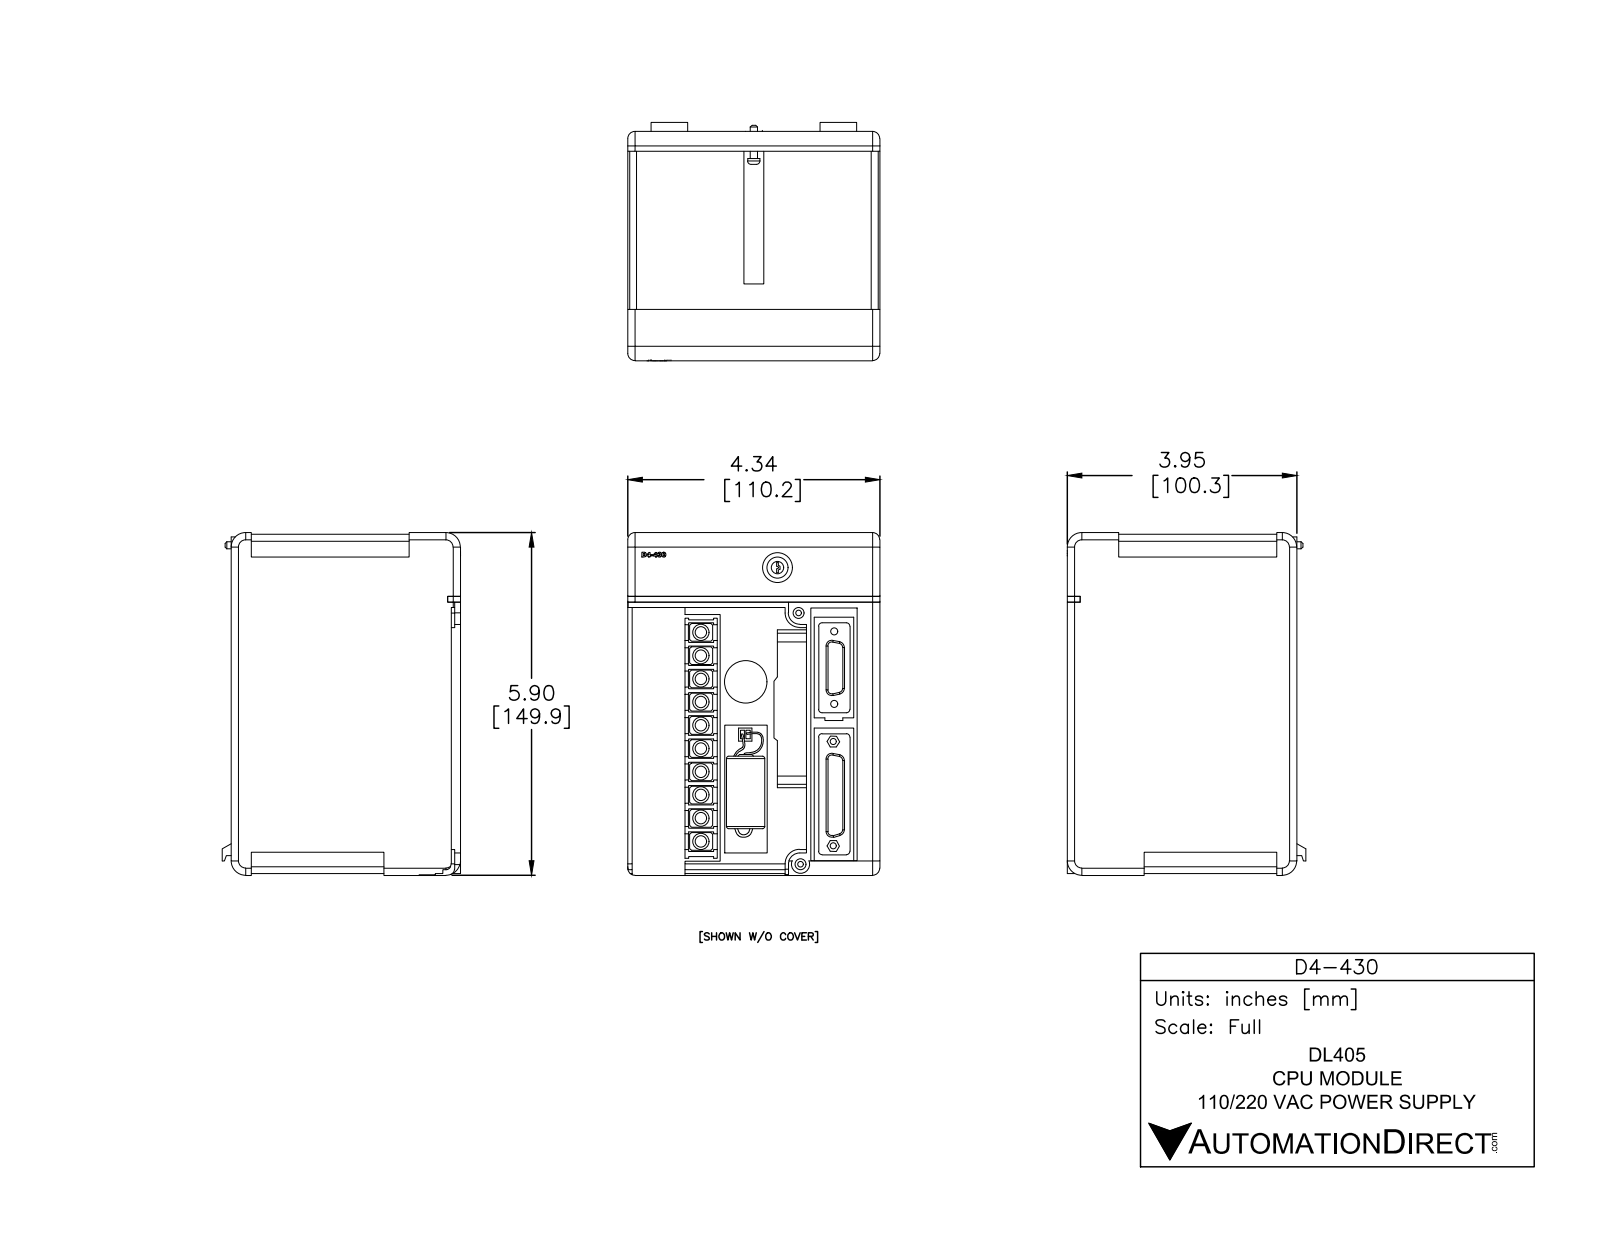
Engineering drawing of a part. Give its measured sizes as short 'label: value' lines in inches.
name: D4-430
written by: SolidWorks 2014 (AUTOMOTIVE_DESIGN)
unit: in
bodies: 2 solids, 755 faces (563 planar, 116 cylindrical, 76 other)
size: 5.905 × 4.34 × 4.106
volume: 90.73 in³; area: 178.4 in²
holes: 2× ⌀0.1, 2× ⌀0.12, 1× ⌀0.104, 1× ⌀0.105, 1× ⌀0.188, 1× ⌀0.188, 1× ⌀0.216, 1× ⌀0.51, 1× ⌀0.73
bosses: 10× ⌀0.279, 1× ⌀0.66, 1× ⌀0.365, 1× ⌀0.212, 1× ⌀0.187, 1× ⌀0.123
rounds: 9× R0.1, 8× R0.06, 8× R0.125, 6× R0.03, 6× R0.25, 4× R0.12, 2× R0.2, 1× R0.031
face distances: 4.34, 0.03, 5.845, 5.875, 3.95, 0.715, 3.235, 0.45, 3.79, 0.555
hole spacings: 0.644, 0.649, 0.69, 0.861, 1.248, 1.47, 1.497, 1.569
